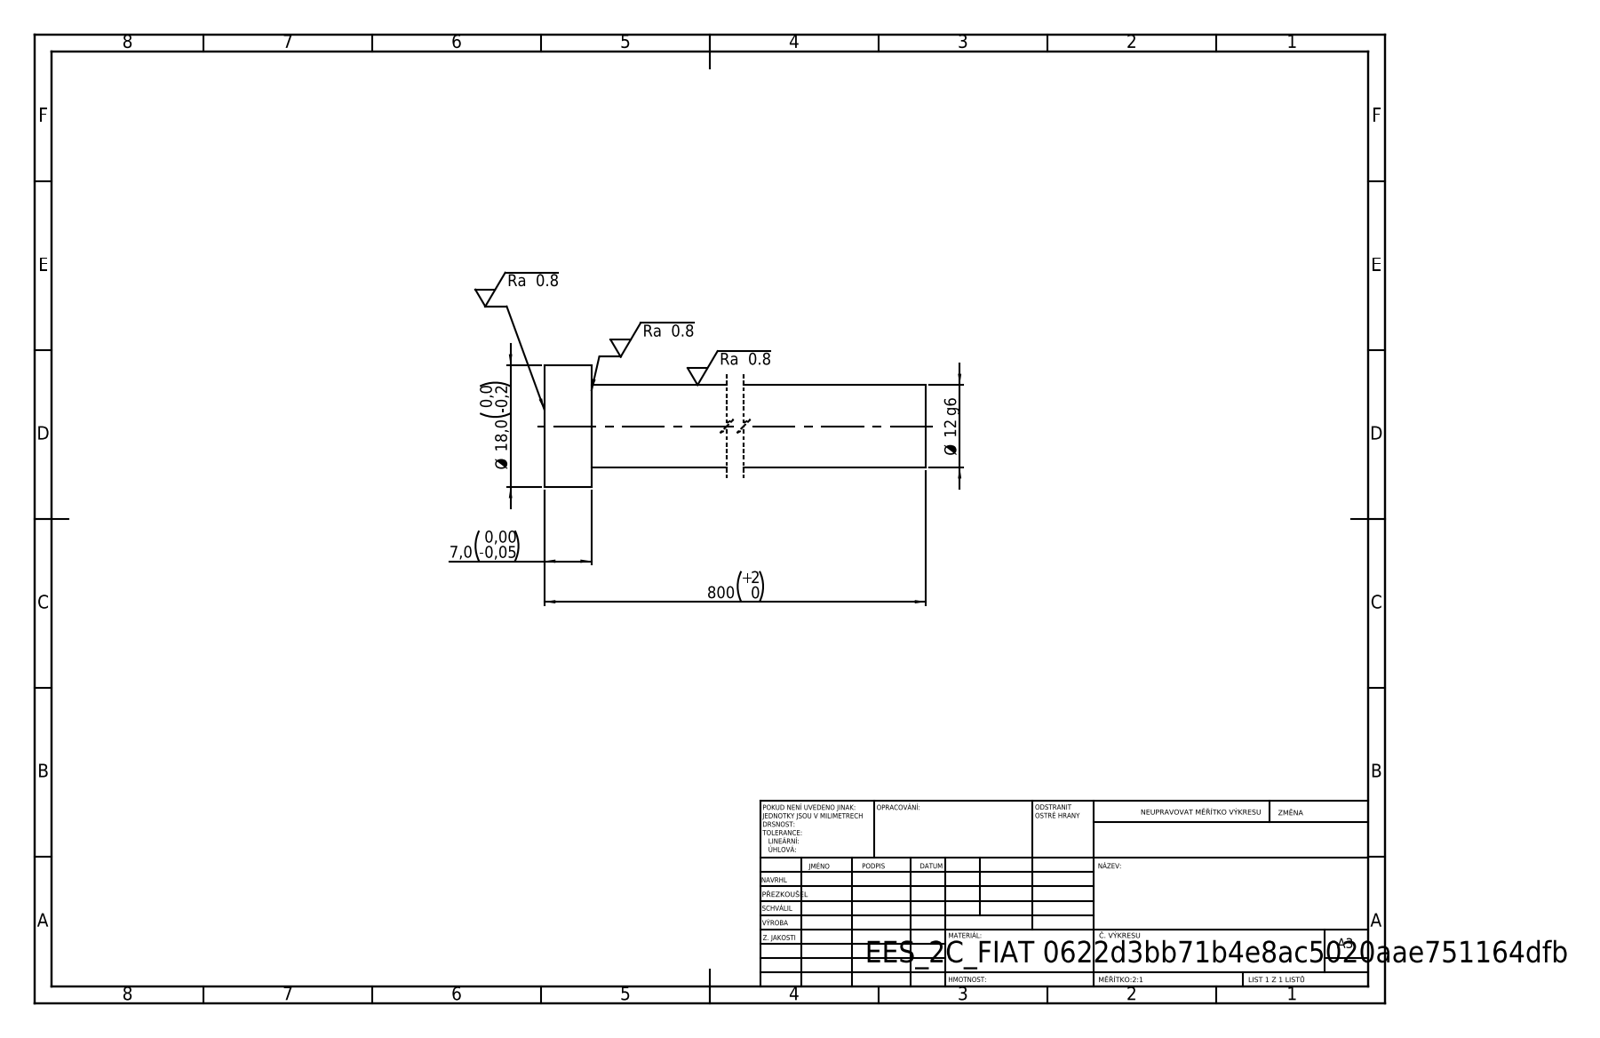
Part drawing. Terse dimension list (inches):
written by: SolidWorks 2019 (CONFIG_CONTROL_DESIGN)
unit: in
bodies: 1 solid, 7 faces (3 planar, 4 cylindrical, 0 other)
size: 31.496 × 0.709 × 0.709
volume: 5.766 in³; area: 48.51 in²
bosses: 1× ⌀0.709, 1× ⌀0.48
face distances: 0.276, 31.496, 31.22
